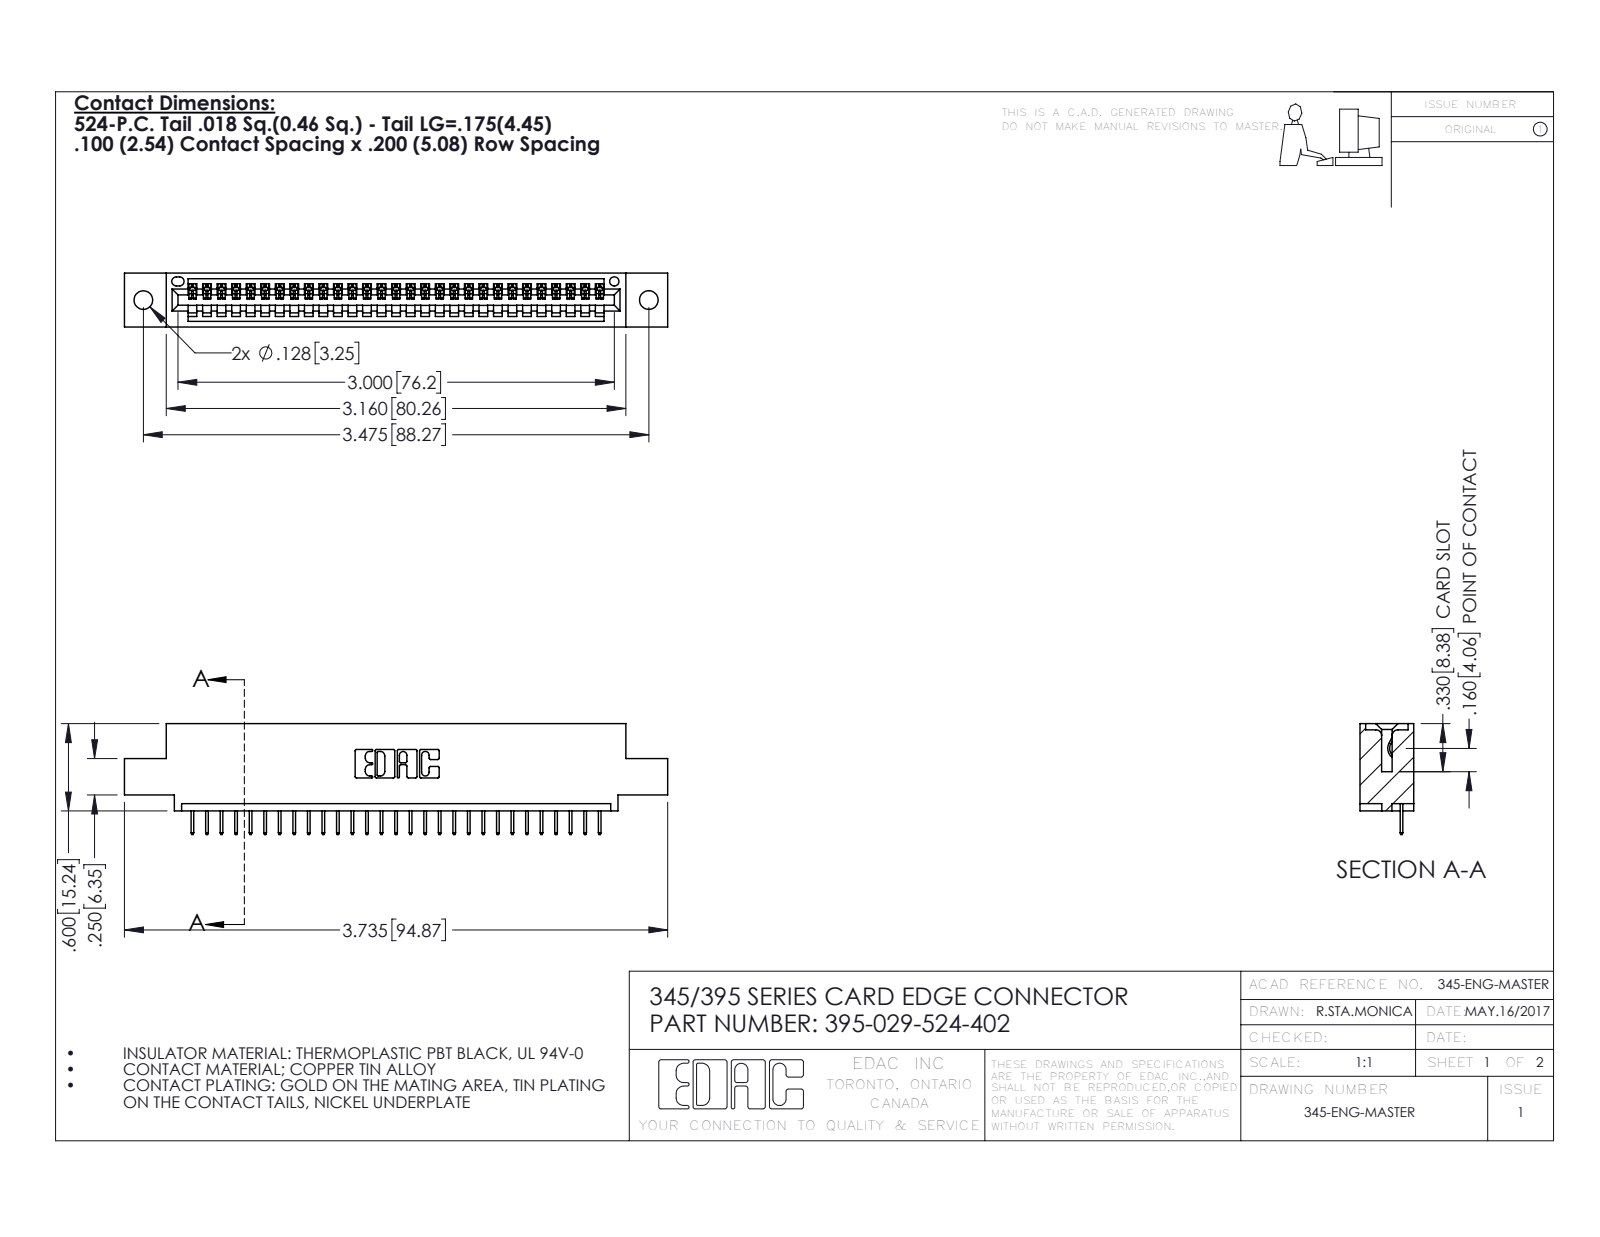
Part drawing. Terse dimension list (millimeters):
name: 395-029-524-402; 345-292-001_345-293-124; 345 Part_0.110 Offset - 0.128 Dia
written by: SolidWorks 2016 (CONFIG_CONTROL_DESIGN)
unit: mm
bodies: 30 solids, 1928 faces (1418 planar, 510 cylindrical, 0 other)
size: 94.9 × 19.4 × 9.4
volume: 8 690 mm³; area: 10 800 mm²
holes: 2× ⌀3.3, 1× ⌀1.6
rounds: 58× R0.2, 22× R0.3, 6× R0.2, 6× R0.8, 3× R0.7, 2× R0.8, 2× R1, 1× R0.4
face distances: 1.8, 7.6, 9.4, 5.1, 2.5, 6.9, 0.6, 5.7, 1.8, 3.8
hole spacings: 6.9, 82.3, 88.3
